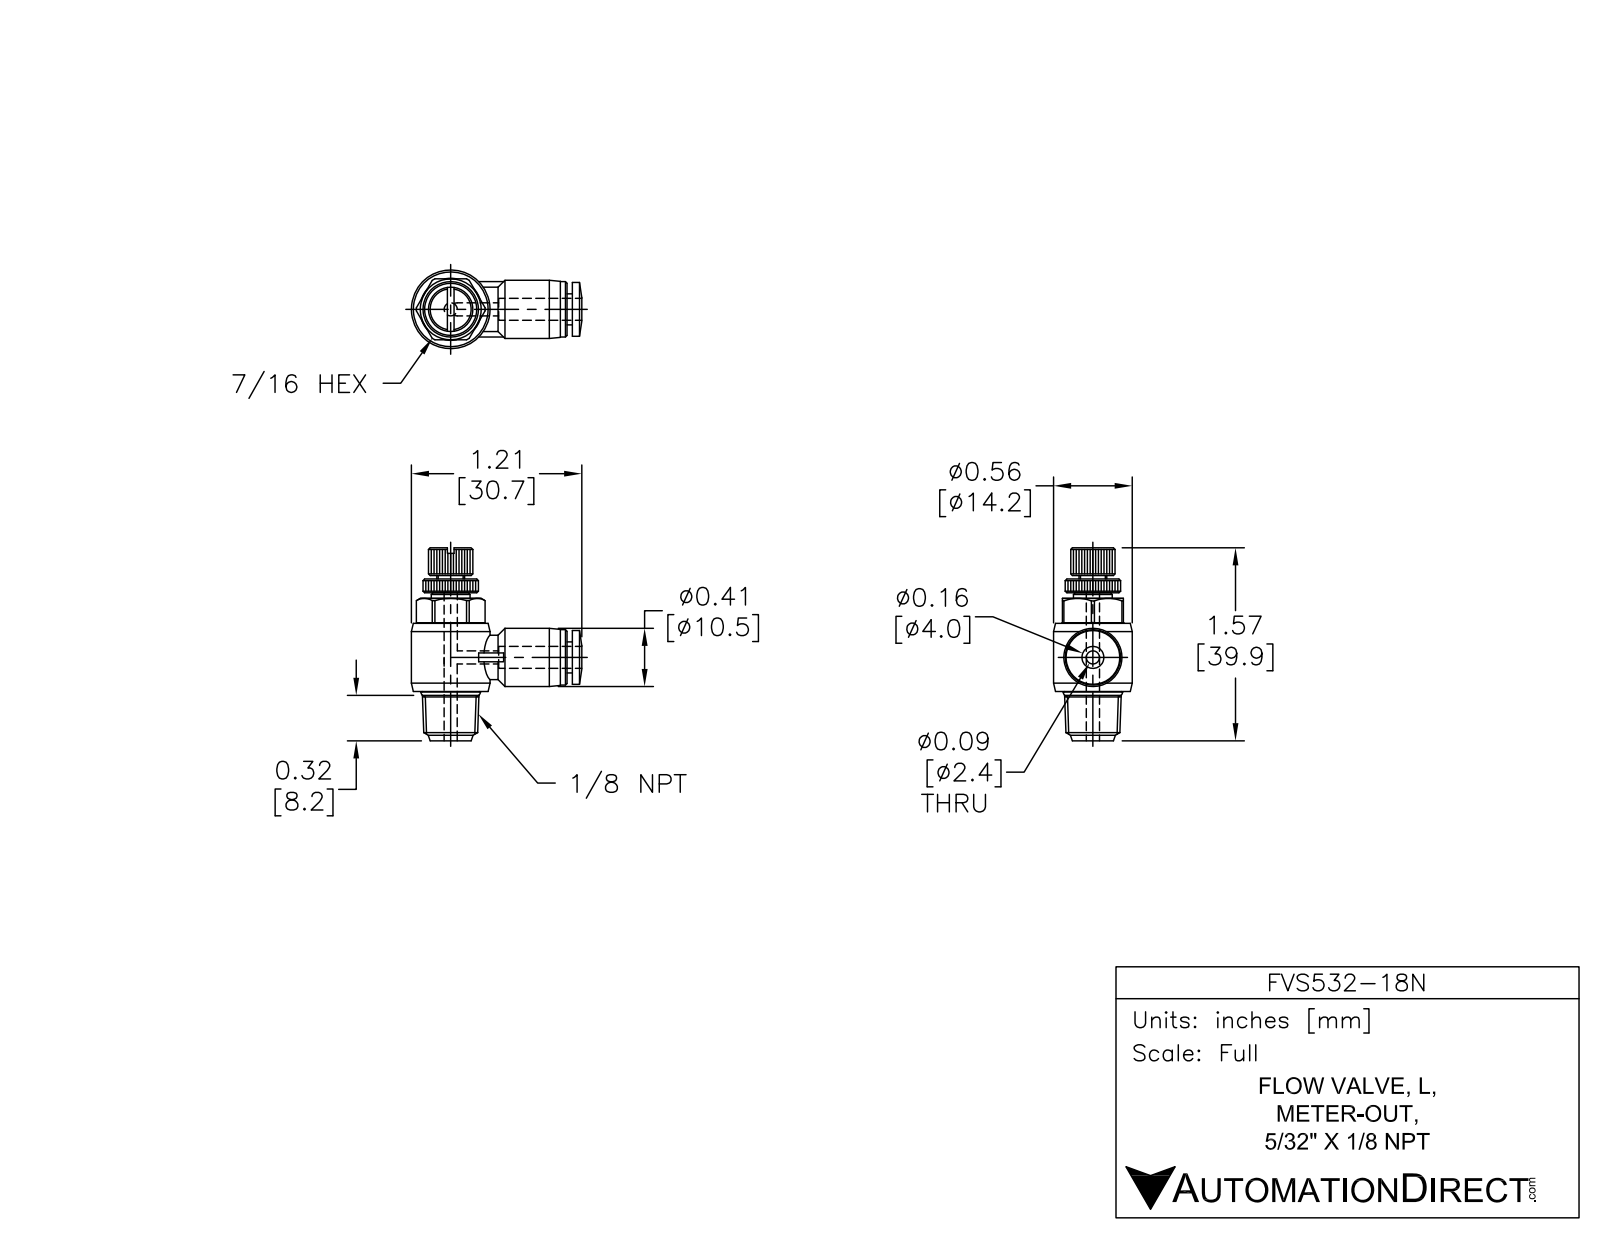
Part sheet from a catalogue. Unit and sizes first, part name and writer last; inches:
Units: inches
Overall size (bounding box): 1.567 × 1.211 × 0.559
Round holes (diameter × count): ⌀0.118 ×2, ⌀0.169 ×1
Round bosses / shafts (diameter × count): ⌀0.559 ×1, ⌀0.441 ×1, ⌀0.413 ×1, ⌀0.406 ×1, ⌀0.394 ×1, ⌀0.388 ×1, ⌀0.315 ×1, ⌀0.276 ×1
Partial cylindrical surfaces — rounded edges, fillets, slot ends (radius × count): R0.157 ×1, R0.197 ×1, R0.244 ×1
Main face-to-face distances: 0.433, 0.661, 0.206, 0.799, 0.138, 0.039, 0.037, 0.484, 0.177, 0.315
Volume: 0.275 in³ · Surface area: 4.424 in²
Bodies: 1 solid, 505 faces (199 planar, 112 cylindrical, 194 other)
Part name (STEP PRODUCT): FVS532-18N
STEP written by: SolidWorks 2015 (AUTOMOTIVE_DESIGN)
